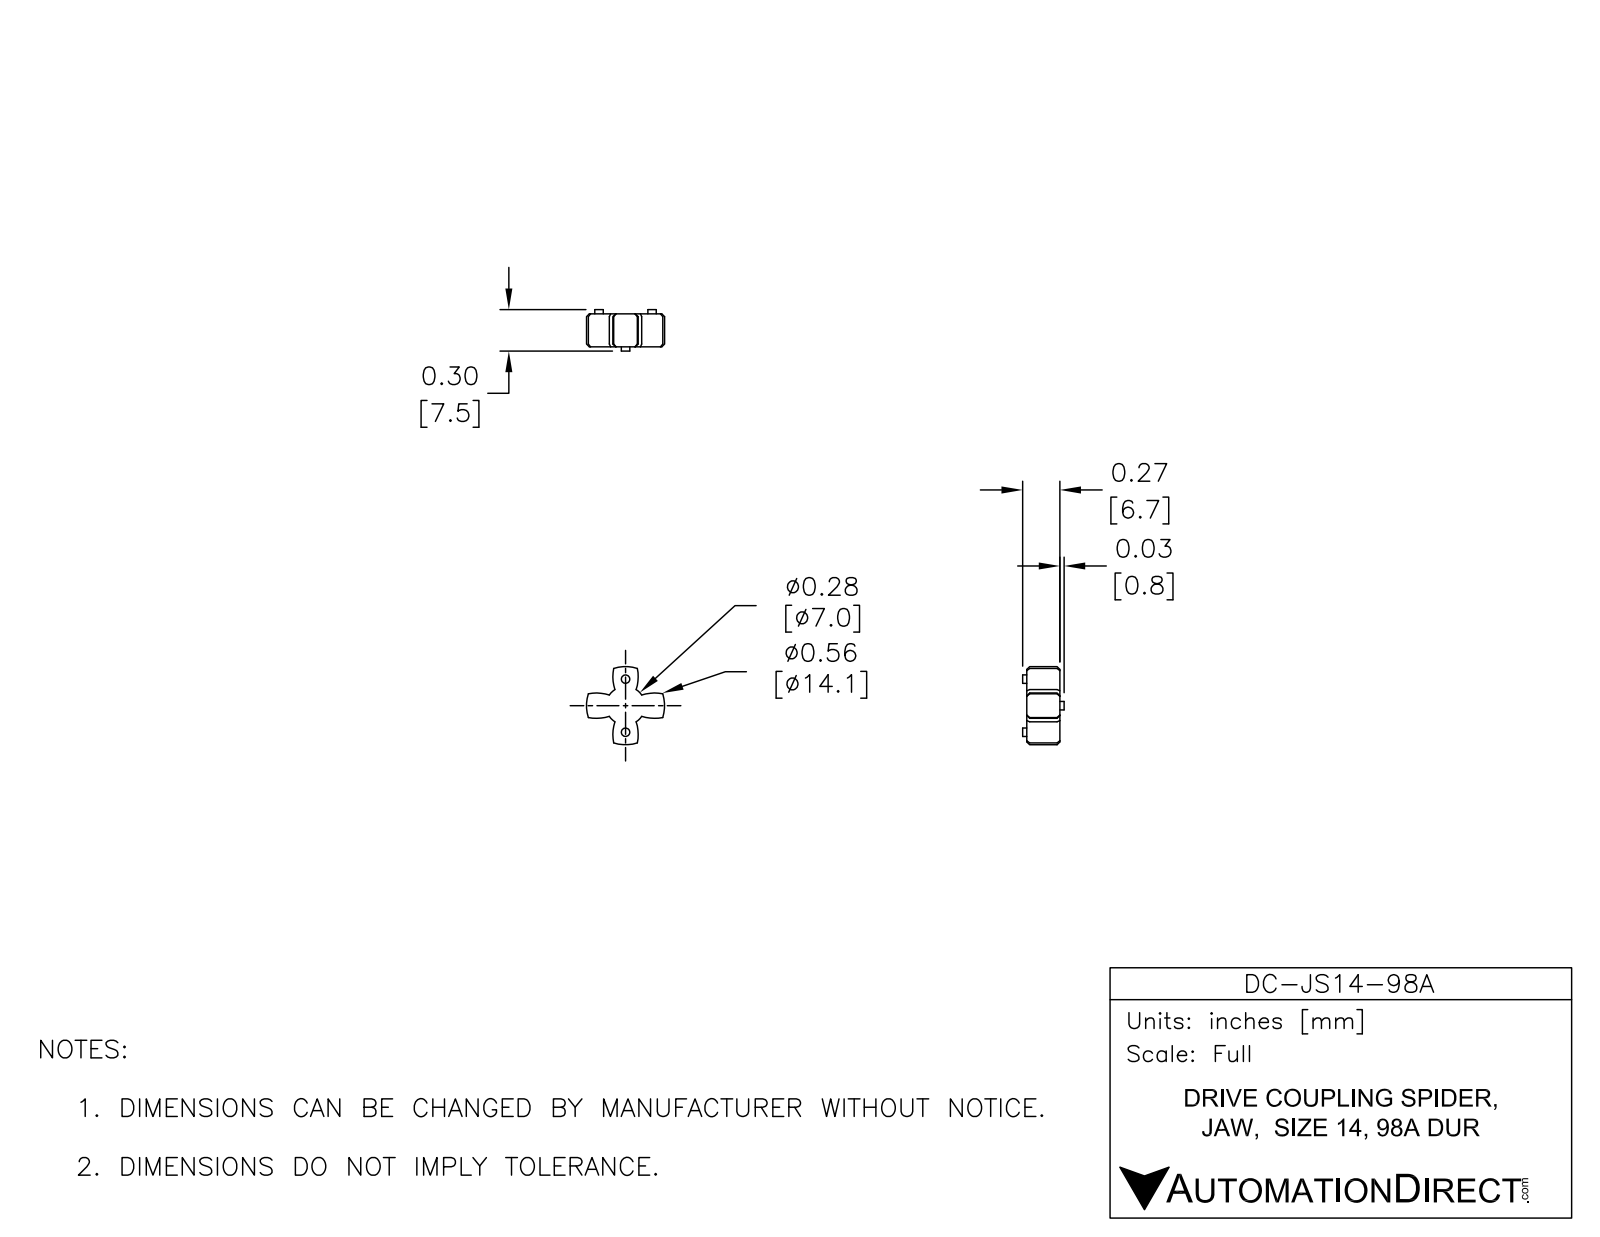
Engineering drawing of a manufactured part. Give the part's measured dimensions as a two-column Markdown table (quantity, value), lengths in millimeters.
| quantity | value |
| --- | --- |
| part name | DC-JS14-98A |
| STEP written by | SolidWorks 2015 (AUTOMOTIVE_DESIGN) |
| units | millimeters |
| bodies | 1 solid, 71 faces (6 planar, 27 cylindrical, 38 other) |
| overall size | 14.1 × 14.1 × 7.49 |
| volume | 605 mm³ |
| surface area | 509 mm² |
| round bosses / shafts (diameter × count) | 1.52 × 4 |
| partial cylindrical surfaces (radius × count) | 7.52 × 4, 3.49 × 1, 7.05 × 1 |
| main face-to-face distances | 5.96, 0.77, 6.73, 7.5 |
